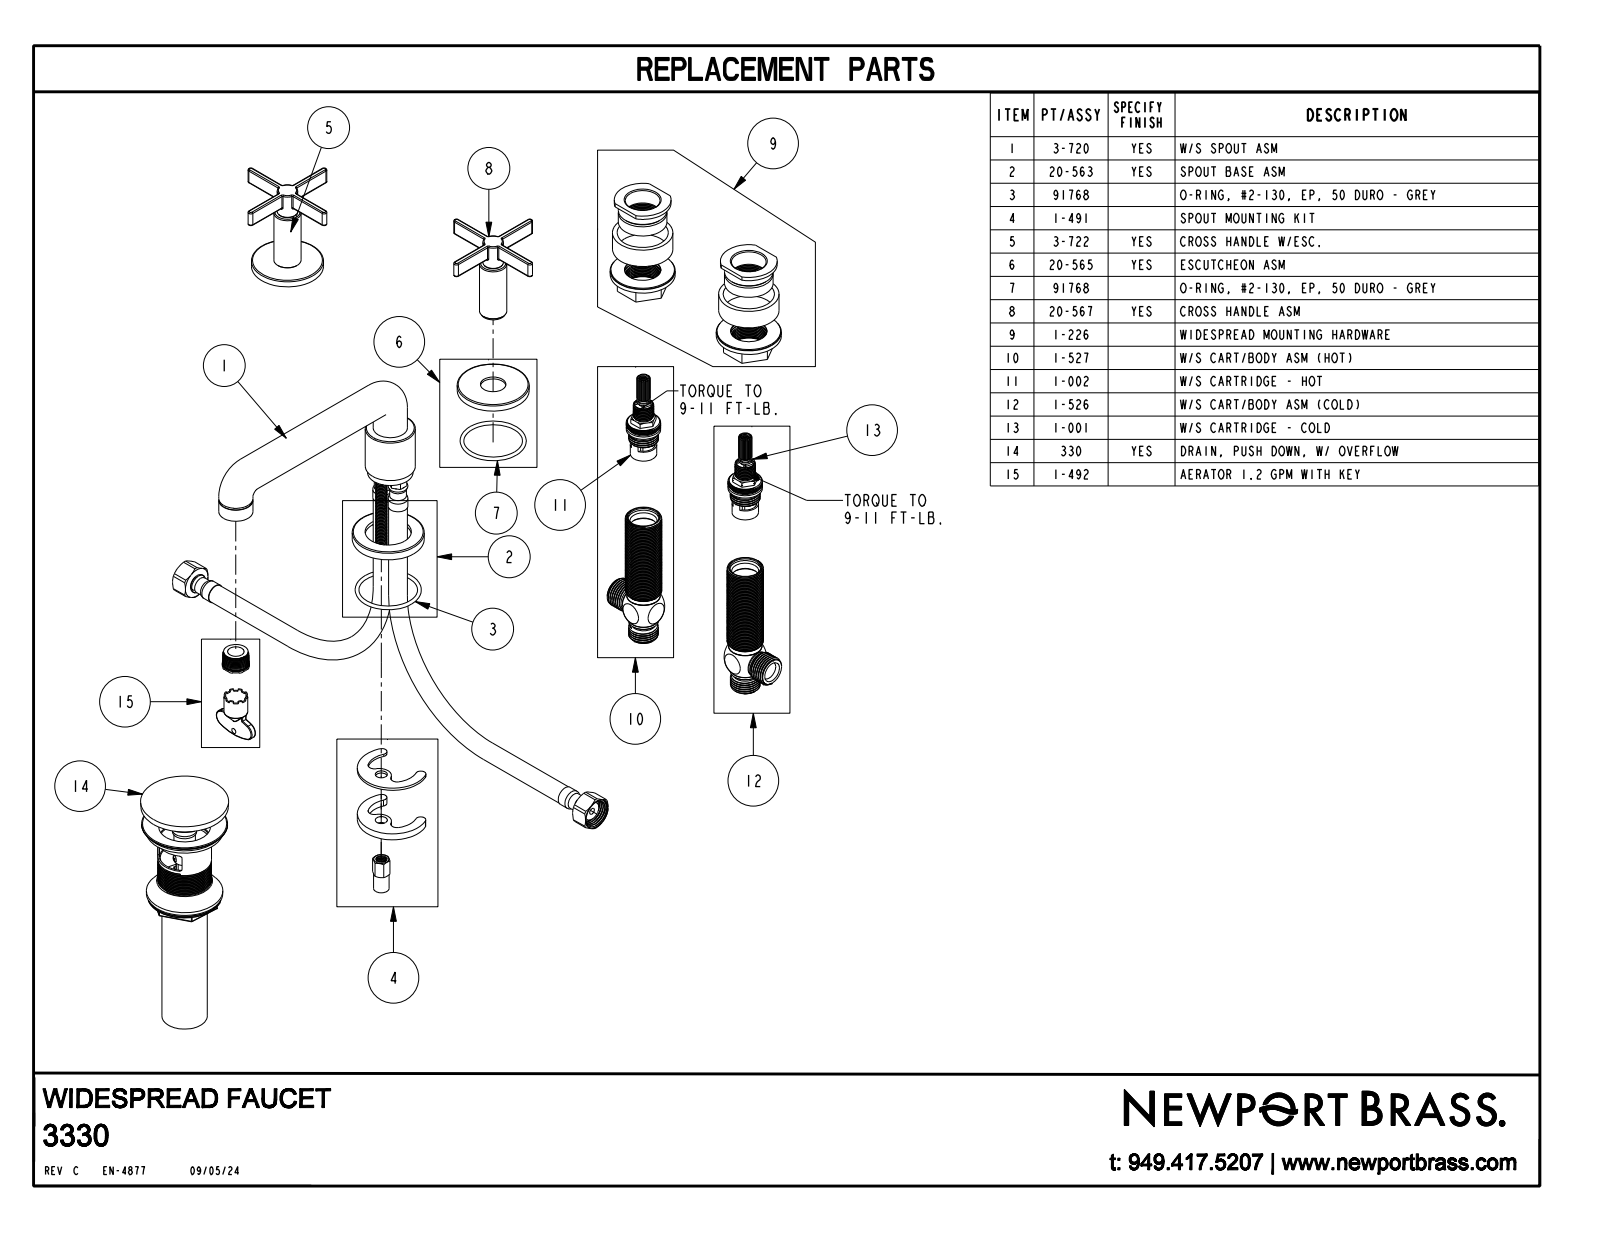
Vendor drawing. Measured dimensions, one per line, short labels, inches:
name: 13530; 20-563_ASM; 13531; 30689 (+8 more)
written by: CREO PARAMETRIC BY PTC INC, 2018400 (CONFIG_CONTROL_DESIGN)
unit: in
bodies: 10 solids, 804 faces (204 planar, 375 cylindrical, 225 other)
size: 11 × 7.976 × 3.211
volume: 7.007 in³; area: 115.3 in²
holes: 3× ⌀0.679, 3× ⌀1.6, 2× ⌀0.11, 2× ⌀0.25, 2× ⌀0.354, 2× ⌀0.36, 2× ⌀0.397, 2× ⌀0.4, 2× ⌀0.423, 2× ⌀0.516, 2× ⌀0.535, 2× ⌀0.6
bosses: 3× ⌀0.939, 3× ⌀0.75, 2× ⌀2, 2× ⌀1.65, 2× ⌀0.73, 2× ⌀0.68, 2× ⌀0.563, 2× ⌀0.51
rounds: 28× R0.03, 8× R0.075, 2× R0.137
face distances: 0.05, 0.15, 0.1, 0.2, 0.07, 0.12, 0.17, 0.25, 0.15, 8
hole spacings: 0.3, 0.461, 3.7, 4, 4.015, 4.3, 6.015, 7.217
